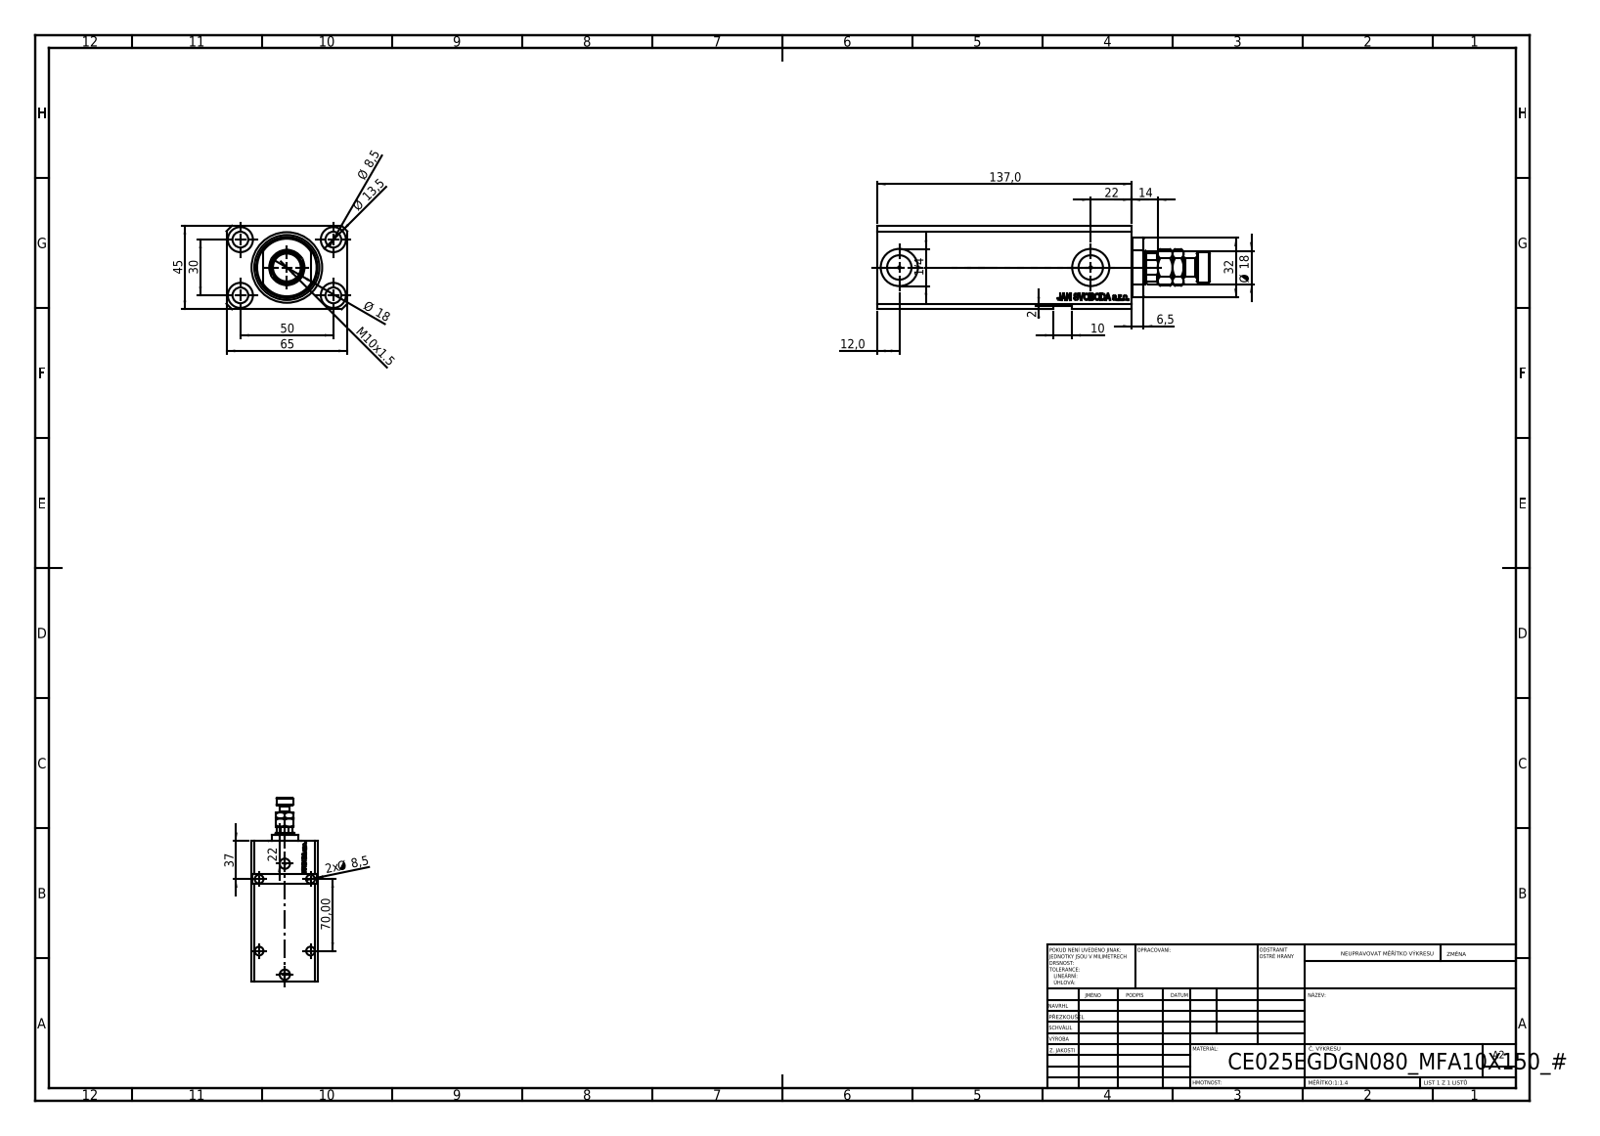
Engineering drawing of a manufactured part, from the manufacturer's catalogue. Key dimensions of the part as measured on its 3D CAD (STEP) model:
Part name (STEP PRODUCT): MFA; V250CE_E_Body; V250CE_C_VCP; V250CE_VC_E
STEP written by: SolidWorks 2019 (CONFIG_CONTROL_DESIGN)
Units: millimetres
Bodies: 4 solids, 985 faces (455 planar, 120 cylindrical, 410 other)
Overall size (bounding box): 179 × 65 × 45
Volume: 336 671 mm³ · Surface area: 83 773 mm²
Round holes (diameter × count): ⌀8.5 ×9, ⌀1.25 ×4, ⌀13.5 ×4, ⌀10 ×2, ⌀13.16 ×2, ⌀20 ×2, ⌀18 ×1, ⌀25 ×1, ⌀38 ×1
Round bosses / shafts (diameter × count): ⌀16 ×1, ⌀10 ×1
Partial cylindrical surfaces — rounded edges, fillets, slot ends (radius × count): R8.5 ×1, R16 ×1
Main face-to-face distances: 45, 65, 14, 123, 137, 6.9, 116.1, 130.1, 28, 43
Hole centre spacings: 29.15, 50, 30, 33.61, 33.97, 58.31, 70, 86.02
